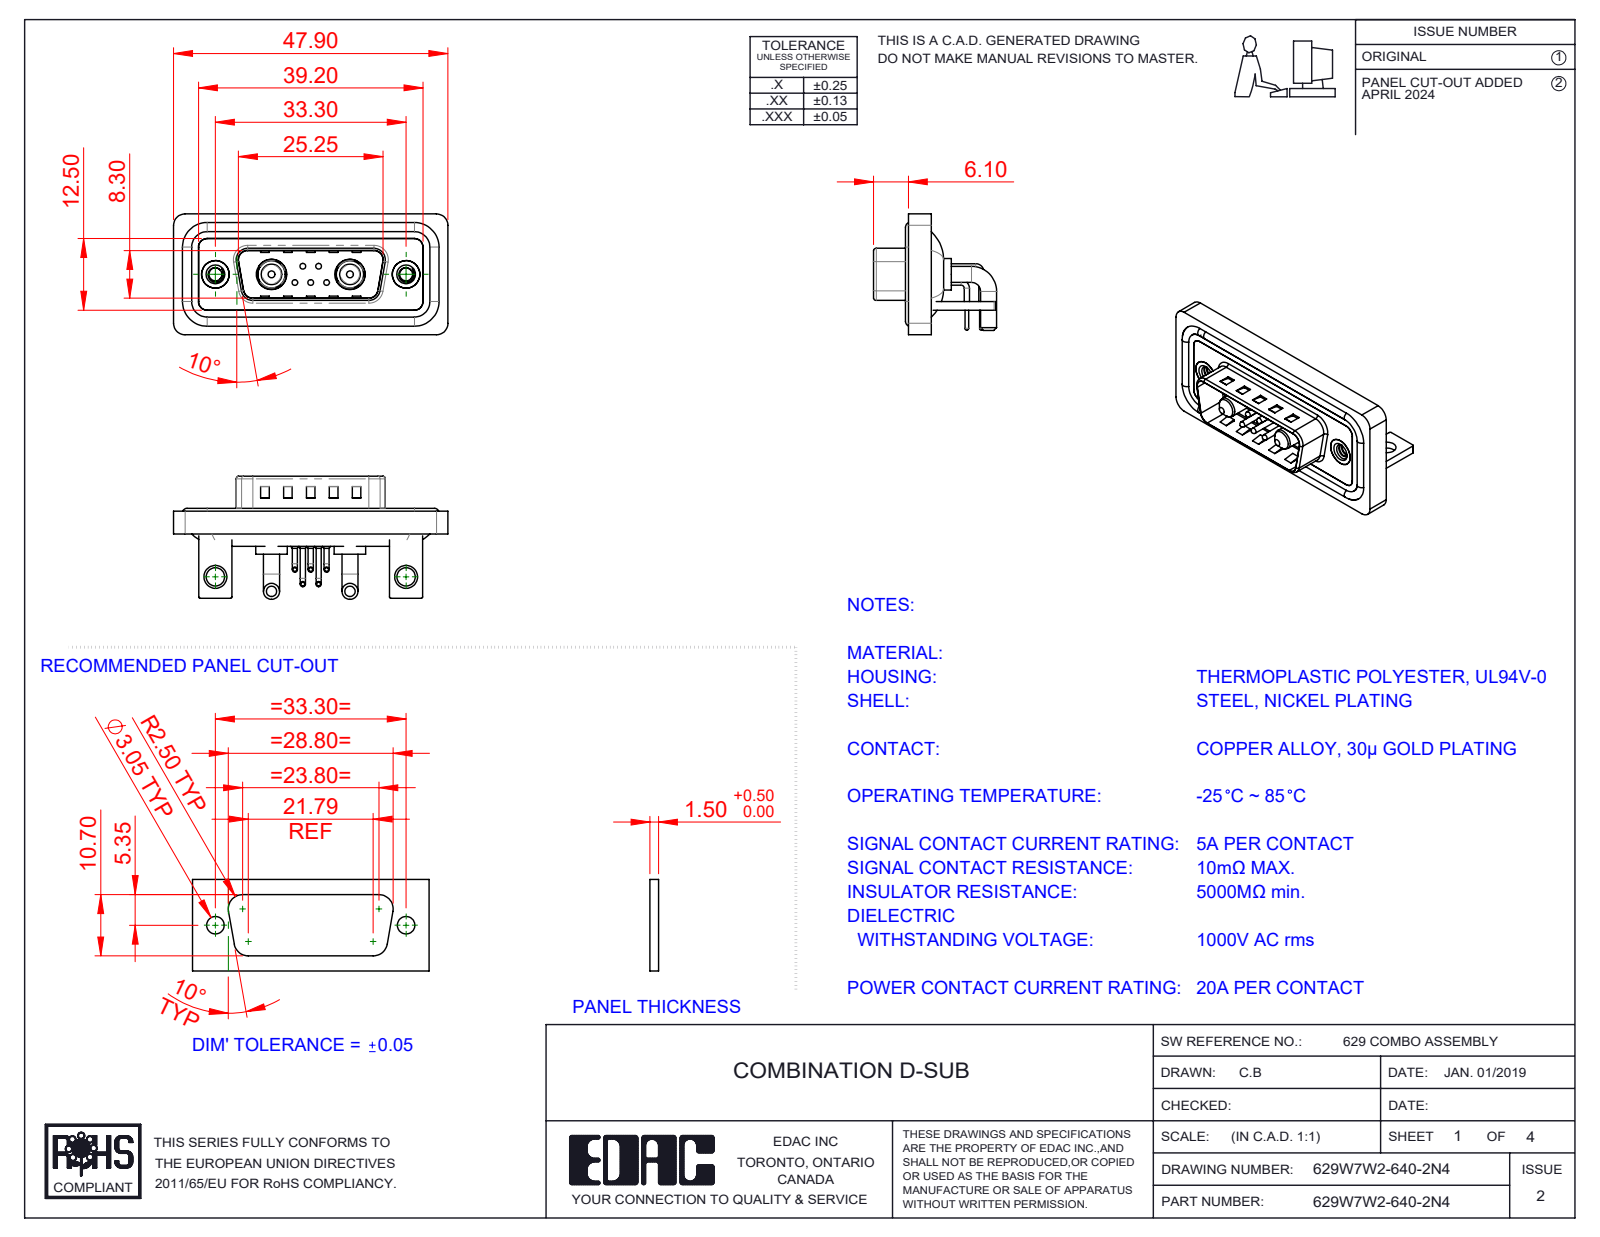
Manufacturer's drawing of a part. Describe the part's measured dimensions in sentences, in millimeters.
The part is named "629Combo Shell Front_15 Contacts; 629Combo Housing_7W2; 629Combo Stabilizer Bracket; 629Combo Contact Row 1 (+6 more)". Its 3-D file was written by "SolidWorks 2023 (CONFIG_CONTROL_DESIGN)". It is 18 solids with 1123 faces: 537 planar, 424 cylindrical and 162 other. Overall it measures 47.9 by 21.5 by 21.1 millimeters. Its volume is 5 958 cubic millimeters and its surface area 9 727 square millimeters. Round holes: 5 of diameter 0.75, 5 of diameter 1.6, 5 of diameter 2, 2 of diameter 2.26, 2 of diameter 3.2, 2 of diameter 4, 2 of diameter 4.8, 2 of diameter 4.85, 2 of diameter 5, 2 of diameter 5.3. Round bosses or shafts: 10 of diameter 0.9, 5 of diameter 1.5, 5 of diameter 1, 5 of diameter 0.65, 4 of diameter 2.8, 4 of diameter 1.6, 2 of diameter 5.5, 2 of diameter 5.2. Partial cylindrical surfaces (rounded edges, fillets, slot ends): 21 of radius 2, 18 of radius 1.5, 16 of radius 0.25, 9 of radius 0.5, 8 of radius 1.6, 5 of radius 1.01, 4 of radius 0.6, 4 of radius 0.65. The main face-to-face distances are 0.4, 1.5, 0.8, 2.9, 2.1, 1.1, 1.6, 1.2, 3.7, 4.5. The hole center spacings are 3.16, 2.77, 9.8, 23.5, 33.3, 4.31, 4.33, 5.03.
